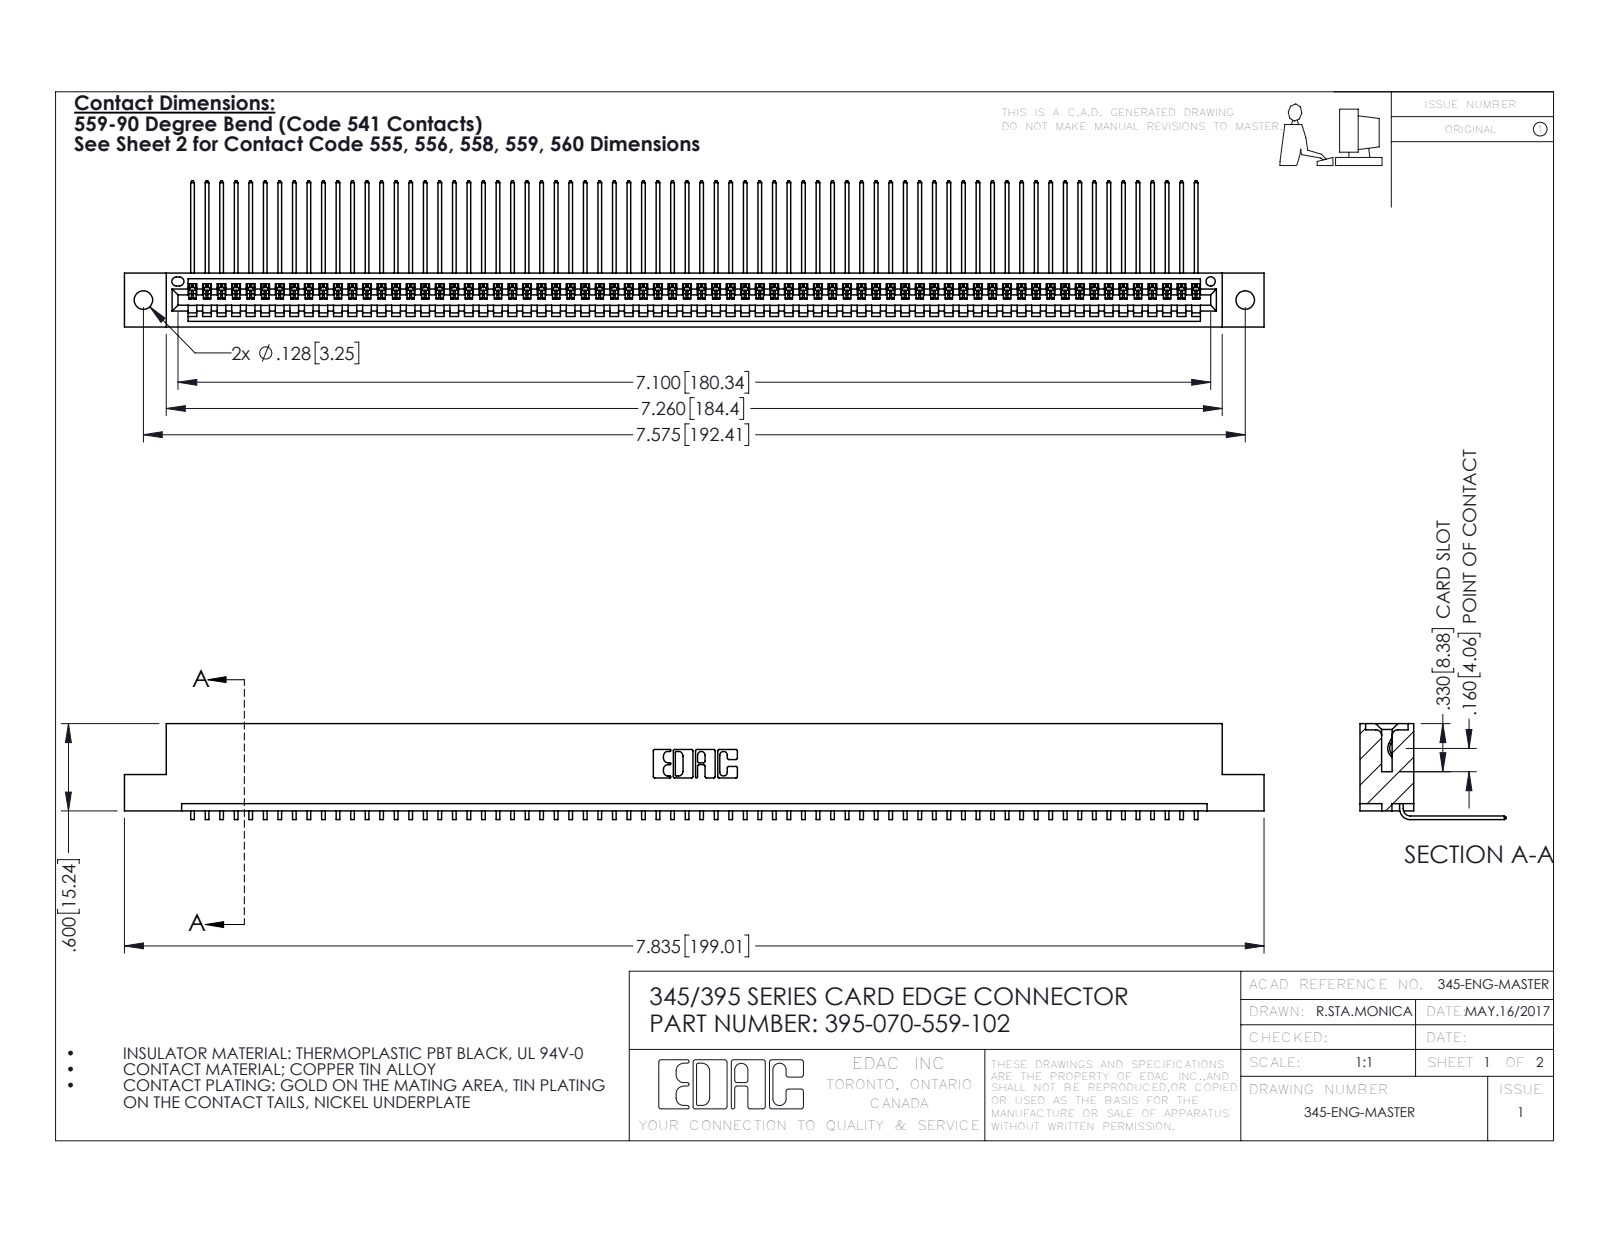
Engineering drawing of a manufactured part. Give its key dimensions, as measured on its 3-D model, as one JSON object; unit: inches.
{"part_name": "345-292-001_558 559 Tail - 1; 395-070-559-102; 345 Part_Flush Mounting Lugs - 0.128 Dia", "step_written_by": "SolidWorks 2016 (CONFIG_CONTROL_DESIGN)", "units": "inches", "bodies": {"solids": 71, "faces": 4326, "planar": 3020, "cylindrical": 1306, "other": 0}, "overall_size": [7.835, 1.005, 0.659], "volume_in3": 1.179, "surface_area_in2": 42.11, "round_holes": [[0.128, 2], [0.064, 1]], "partial_cylinders_radius": [[0.006, 140], [0.01, 22], [0.007, 6], [0.031, 6], [0.026, 3], [0.031, 2], [0.04, 2], [0.014, 1]], "face_to_face_distances": [0.298, 0.072, 0.37, 0.2, 0.098, 0.272, 0.025, 0.225, 0.149, 0.072], "hole_center_spacings": [0.27, 7.339, 7.575]}
